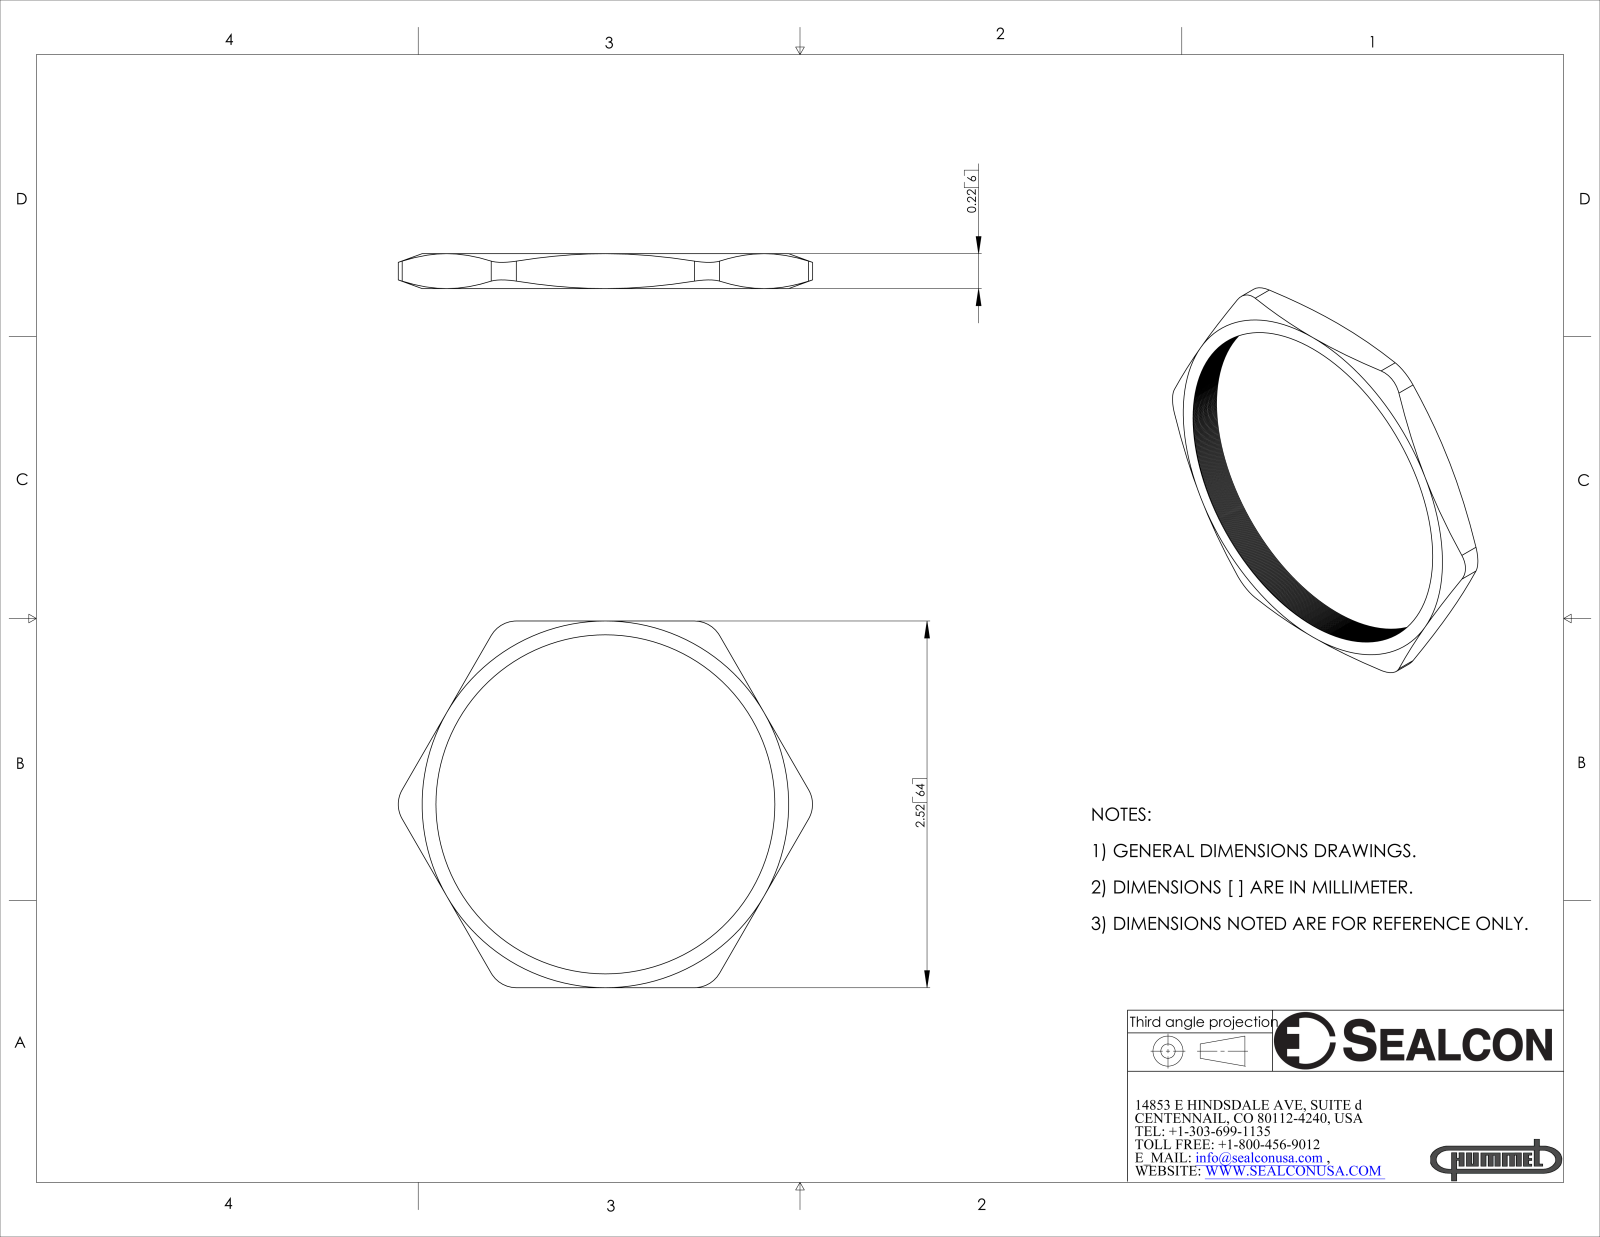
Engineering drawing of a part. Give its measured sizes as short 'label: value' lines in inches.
name: NP-48-BR
written by: SolidWorks 2007 (CONFIG_CONTROL_DESIGN)
unit: in
bodies: 1 solid, 147 faces (8 planar, 7 cylindrical, 132 other)
size: 2.848 × 2.52 × 0.24
volume: 0.253 in³; area: 7.621 in²
rounds: 6× R0.2
face distances: 2.52, 0.24
